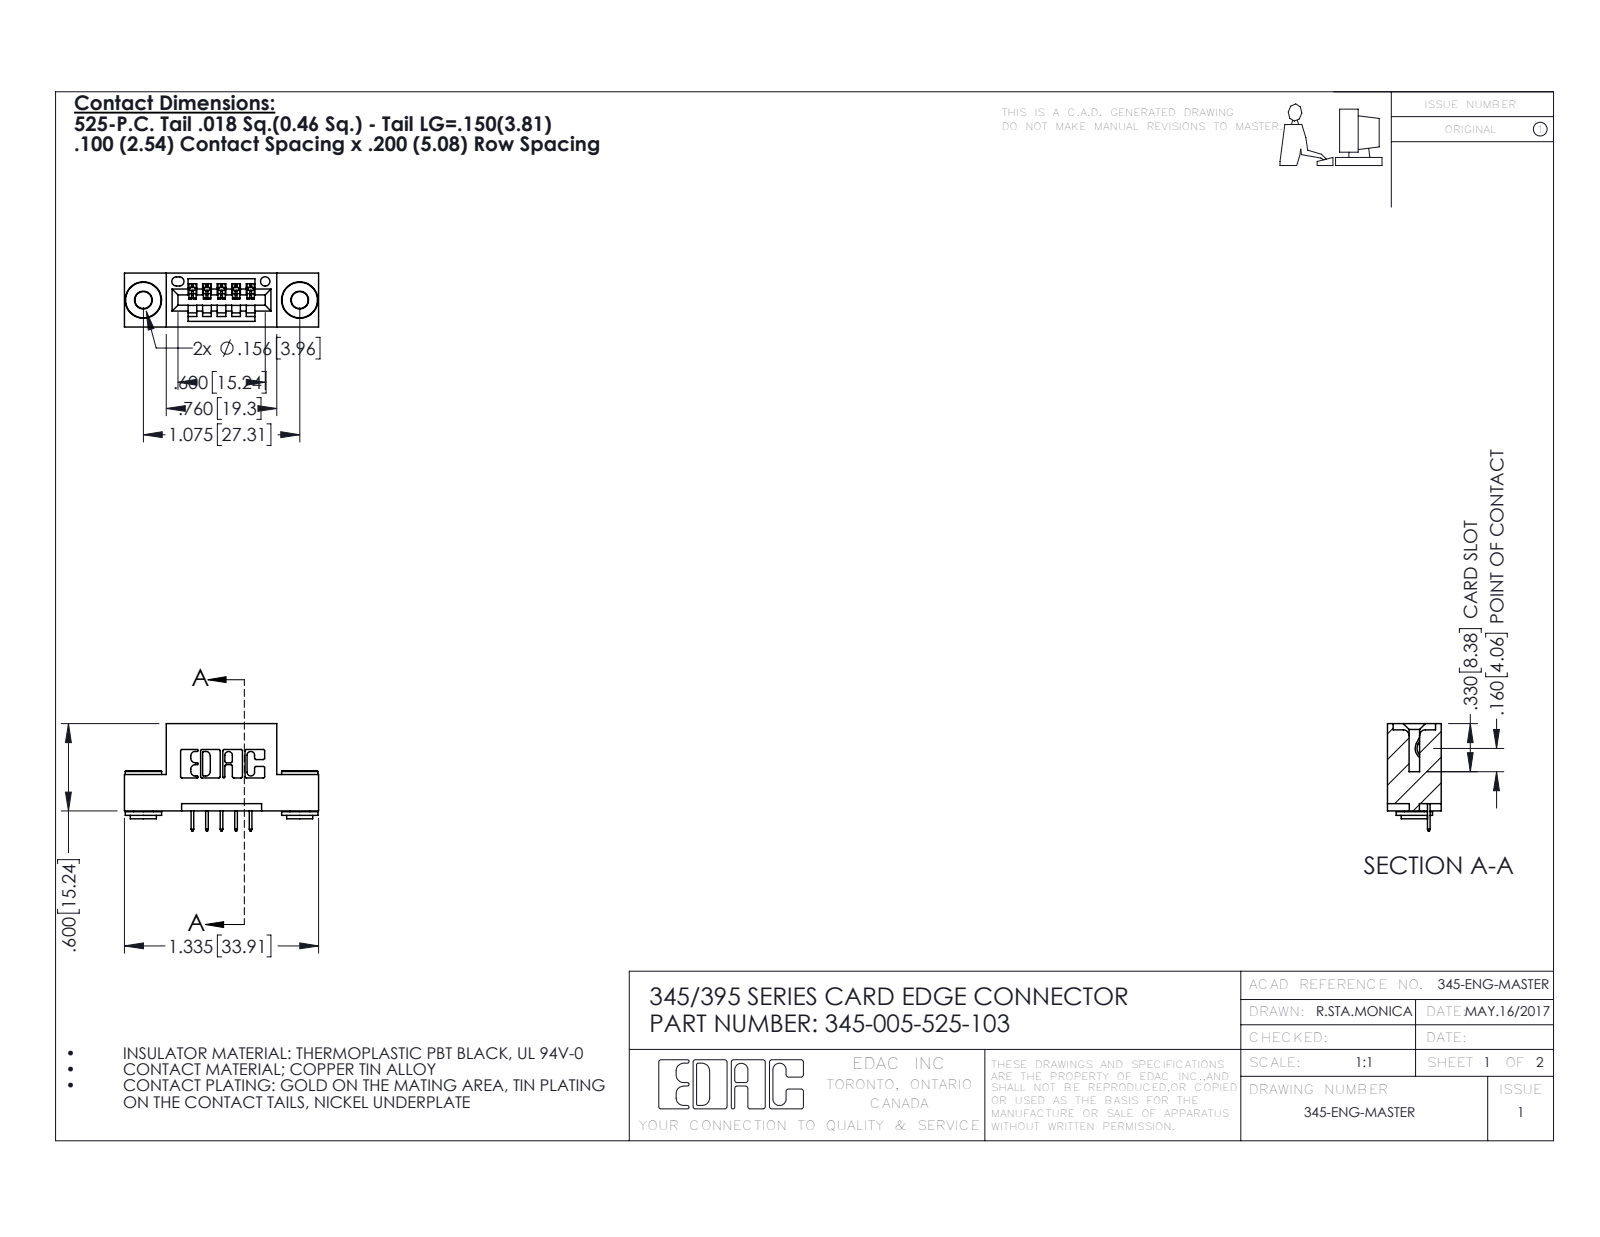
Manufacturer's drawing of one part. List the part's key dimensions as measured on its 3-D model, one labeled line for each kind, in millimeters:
Part name (STEP PRODUCT): 345-292-001_345-293-125; 345-250-002_345-250-002-102; 345-005-525-103; 345 Part_Flush Mounting Lugs - 0.156 Dia-TH
STEP written by: SolidWorks 2020 (CONFIG_CONTROL_DESIGN)
Units: millimetres
Bodies: 8 solids, 474 faces (320 planar, 146 cylindrical, 8 other)
Overall size (bounding box): 33.9 × 18.7 × 9.4
Volume: 2 920 mm³ · Surface area: 3 519 mm²
Round holes (diameter × count): ⌀2.9 ×2, ⌀4 ×2, ⌀1.6 ×1
Round bosses / shafts (diameter × count): ⌀6.4 ×2, ⌀4.6 ×2, ⌀3.5 ×2
Partial cylindrical surfaces — rounded edges, fillets, slot ends (radius × count): R0.3 ×22, R0.2 ×10, R0.2 ×6, R0.8 ×6, R0.7 ×3, R0.8 ×2, R1 ×2, R0.4 ×1
Main face-to-face distances: 5.1, 9.4, 2.5, 1.8, 7.6, 6.4, 0.6, 8.9, 1.5, 7.6
Hole centre spacings: 6.9, 21.5, 27.3
